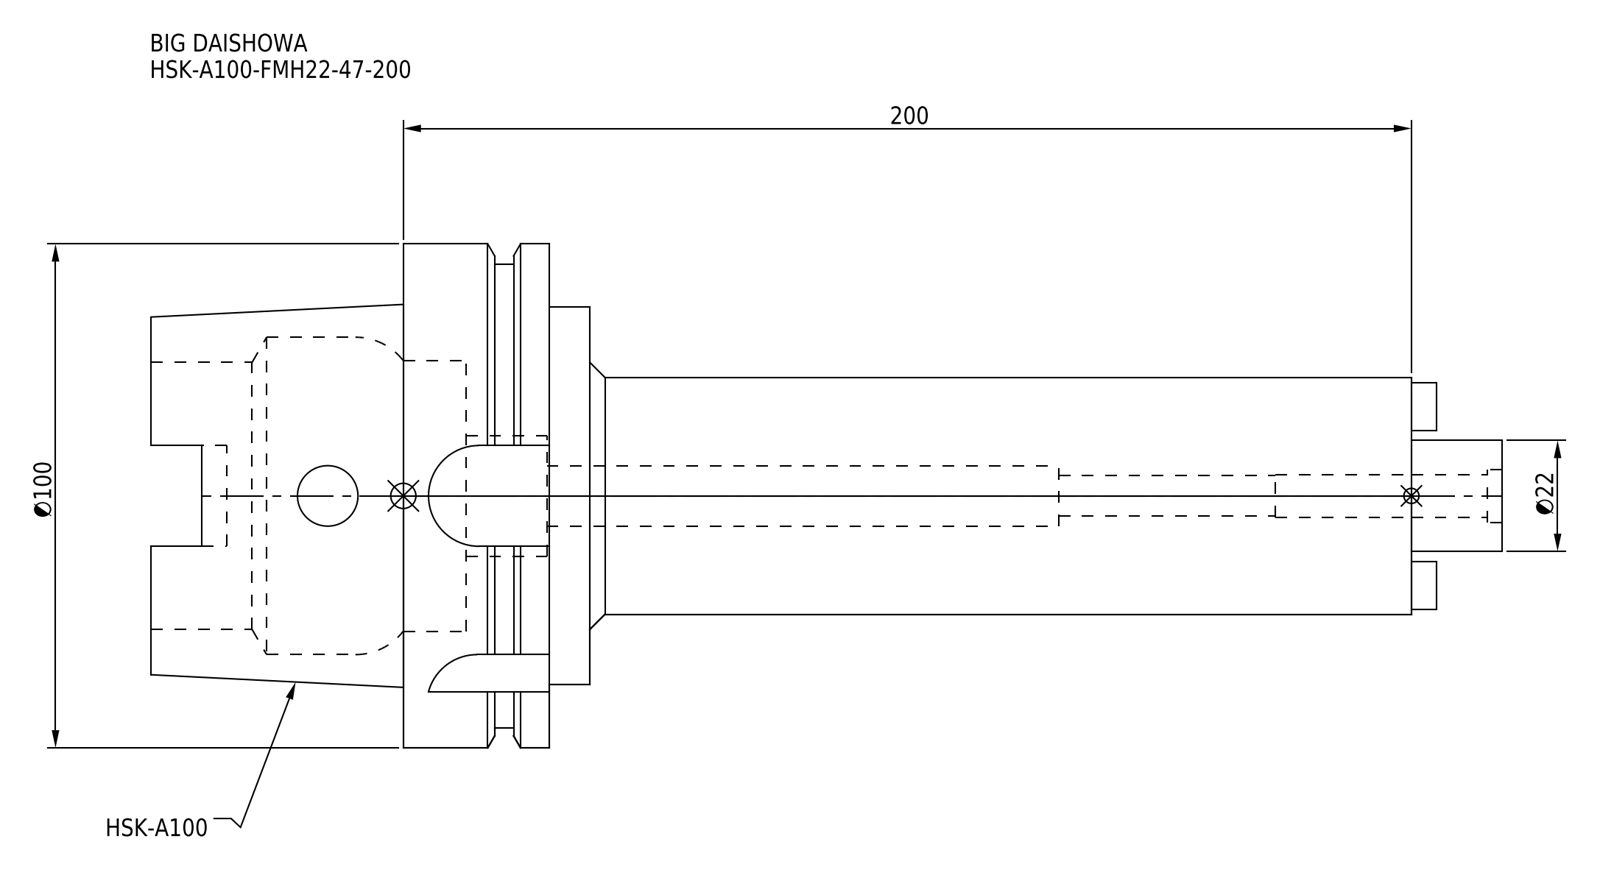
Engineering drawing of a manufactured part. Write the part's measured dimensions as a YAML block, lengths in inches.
part_name: "HSK-A100-FMH22-47-200"
step_written_by: "CREO PARAMETRIC BY PTC INC, 2016380 (AUTOMOTIVE_DESIGN)"
units: inches
bodies: {solids: 1, faces: 109, planar: 47, cylindrical: 46, other: 16}
overall_size: [10.551, 3.937, 3.937]
volume: 34.41
surface_area: 129.2
round_holes:
  - {diameter: 0.472, count: 2}
  - {diameter: 0.315, count: 1}
  - {diameter: 0.335, count: 1}
  - {diameter: 0.413, count: 1}
  - {diameter: 0.945, count: 1}
  - {diameter: 2.087, count: 1}
  - {diameter: 2.118, count: 1}
  - {diameter: 2.48, count: 1}
round_bosses_or_shafts:
  - {diameter: 3.937, count: 1}
  - {diameter: 3.622, count: 1}
  - {diameter: 2.953, count: 1}
  - {diameter: 1.85, count: 1}
  - {diameter: 0.866, count: 1}
partial_cylinders:
  - {radius: 0.192, count: 4}
  - {radius: 0.394, count: 4}
face_to_face_distances: [1.142, 0.315, 1.457, 0.967, 0.652, 0.49, 7.874, 6.417, 6.732, 7.384]
